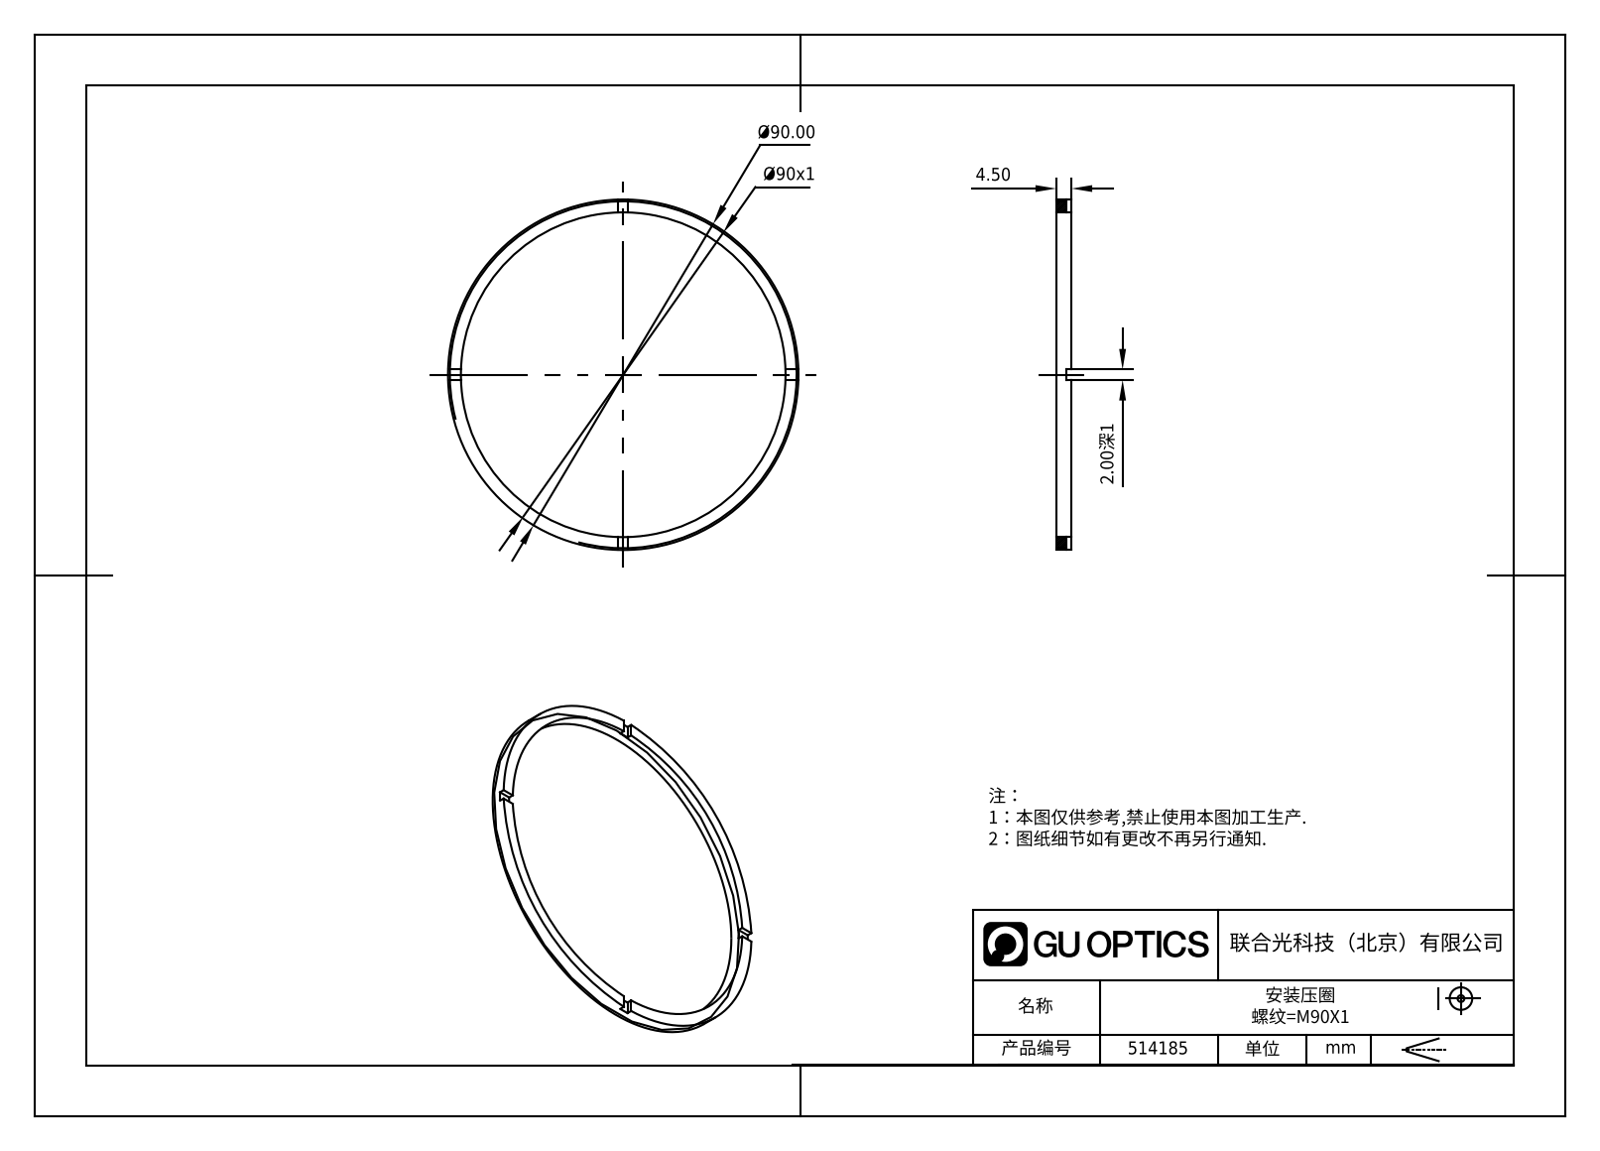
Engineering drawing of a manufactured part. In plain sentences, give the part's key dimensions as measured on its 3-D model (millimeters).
The part is named "514185". Its 3-D file was written by "SolidWorks 2020 (CONFIG_CONTROL_DESIGN)". It is 1 solid with 21 faces: 17 planar, 4 cylindrical and 0 other. Overall it measures 90 by 90 by 4.5 millimeters. Its volume is 4 252 cubic millimeters and its surface area 4 360 square millimeters. Round holes: 1 of diameter 83. Round bosses or shafts: 1 of diameter 90. The main face-to-face distances are 4.5, 3.5, 1, 2.
